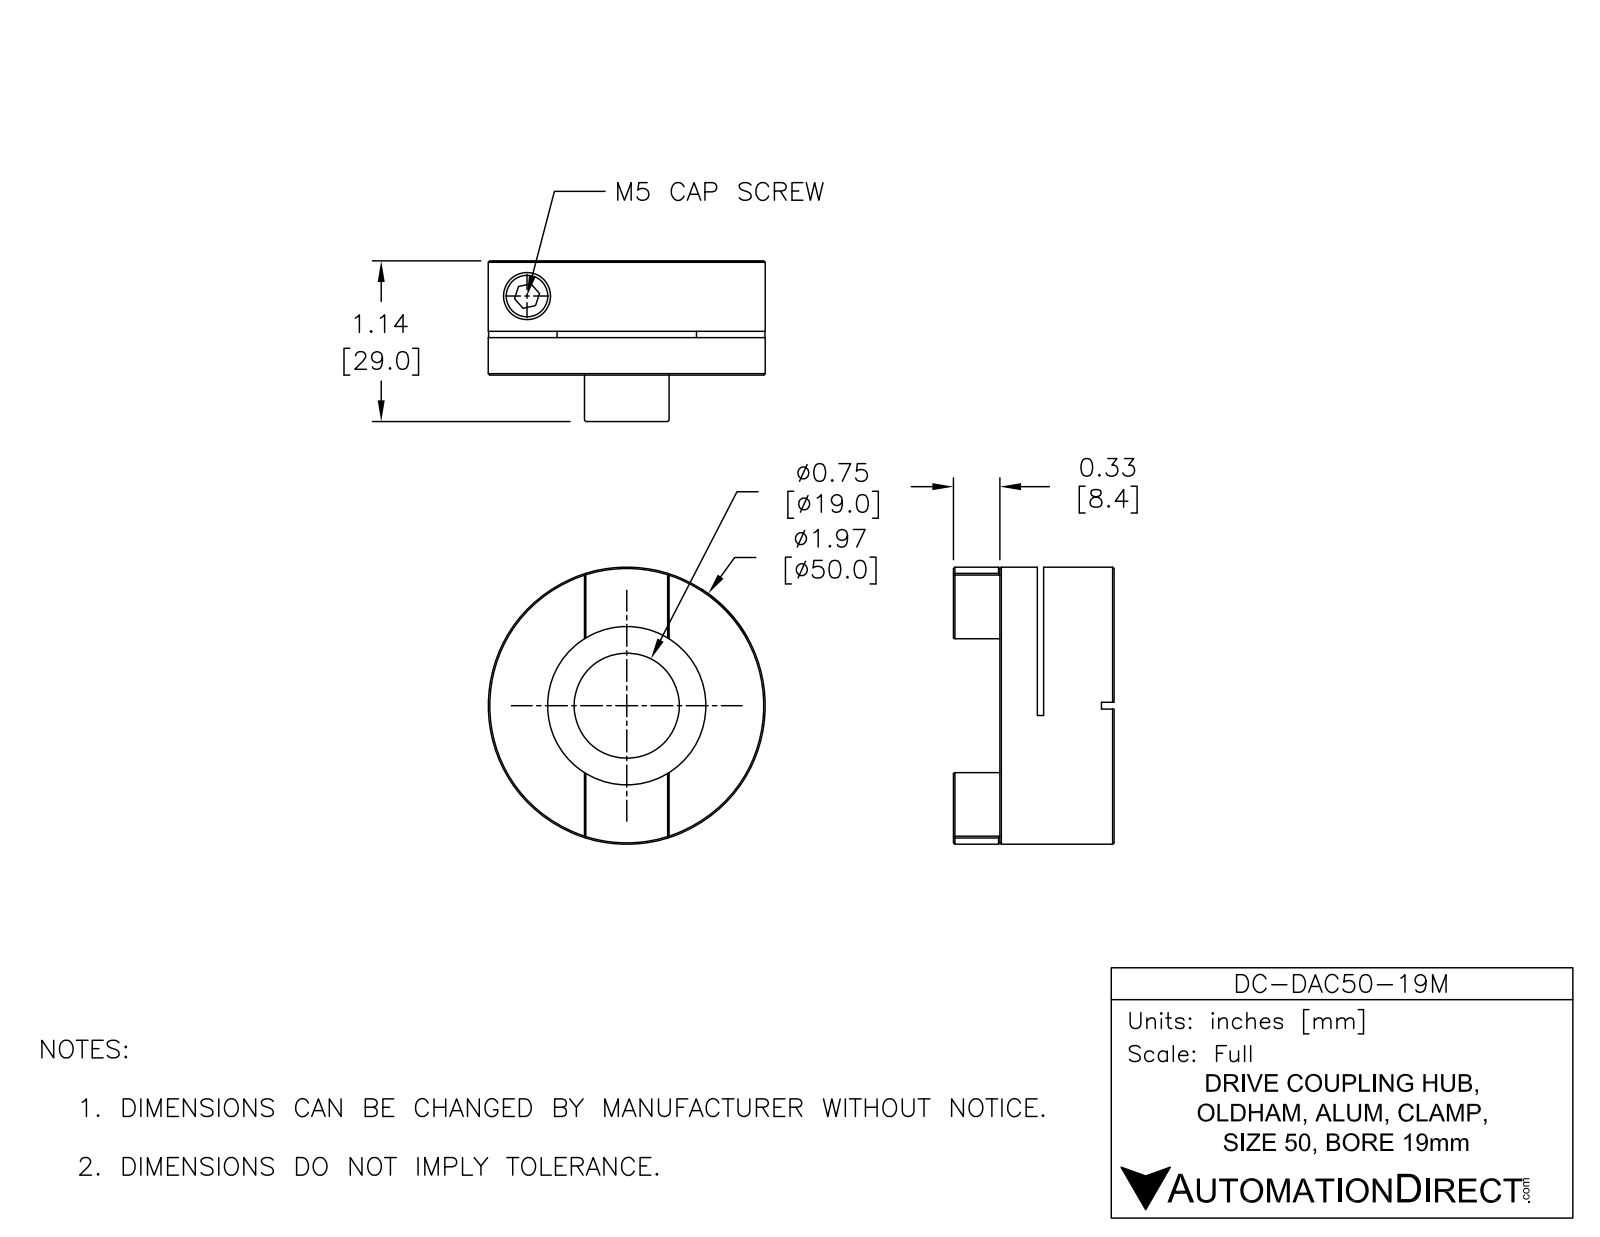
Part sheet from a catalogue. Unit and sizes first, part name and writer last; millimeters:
Units: millimetres
Overall size (bounding box): 50 × 50 × 28.98
Round holes (diameter × count): ⌀5.51 ×1, ⌀10.01 ×1, ⌀19 ×1, ⌀28.57 ×1
Round bosses / shafts (diameter × count): ⌀50 ×1
Partial cylindrical surfaces — rounded edges, fillets, slot ends (radius × count): R25.4 ×1
Main face-to-face distances: 20.6, 13.84, 6.76, 12.7, 1.14, 7.9, 18.82, 6.12, 4.98, 1.78
Volume: 33 779 mm³ · Surface area: 11 642 mm²
Bodies: 1 solid, 57 faces (30 planar, 17 cylindrical, 10 other)
Part name (STEP PRODUCT): DC-DAC50-19M
STEP written by: SolidWorks 2015 (AUTOMOTIVE_DESIGN)
